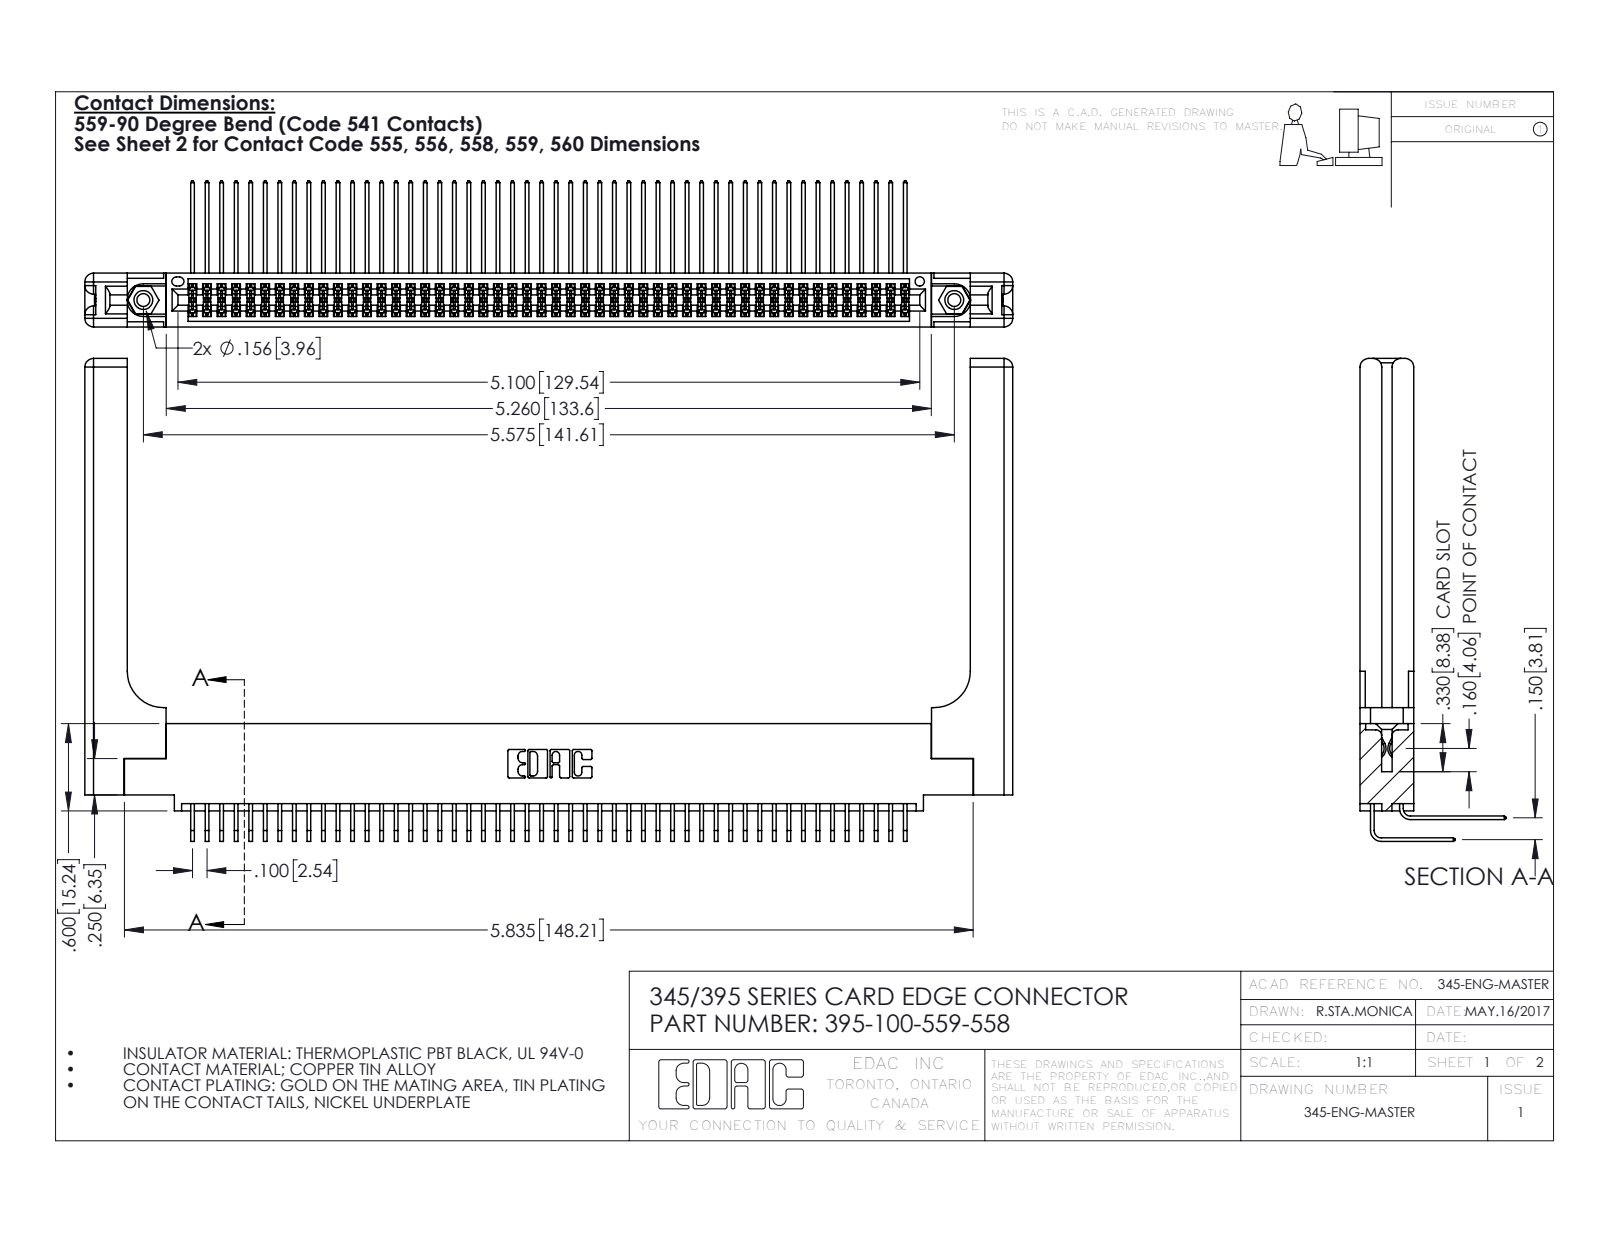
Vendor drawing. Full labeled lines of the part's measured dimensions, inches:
Part name (STEP PRODUCT): 345-220-058_345-220-058; 395-100-559-558; 345-292-001_558 559 Tail - 1; 345-250-001_345-250-001-102 (+2 more)
STEP written by: SolidWorks 2016 (CONFIG_CONTROL_DESIGN)
Units: inches
Bodies: 105 solids, 5586 faces (3732 planar, 1794 cylindrical, 60 other)
Overall size (bounding box): 6.379 × 3.319 × 1.005
Volume: 1.513 in³ · Surface area: 49.82 in²
Round holes (diameter × count): ⌀0.089 ×2, ⌀0.125 ×2, ⌀0.156 ×2, ⌀0.064 ×1
Round bosses / shafts (diameter × count): ⌀0.155 ×2
Partial cylindrical surfaces — rounded edges, fillets, slot ends (radius × count): R0.006 ×151, R0.01 ×22, R0.06 ×16, R0.007 ×6, R0.031 ×6, R0.026 ×3, R0.014 ×2, R0.019 ×2
Main face-to-face distances: 0.072, 0.298, 0.37, 0.098, 0.272, 0.025, 0.2, 0.225, 0.175, 0.15
Hole centre spacings: 0.27, 5.339, 5.575
